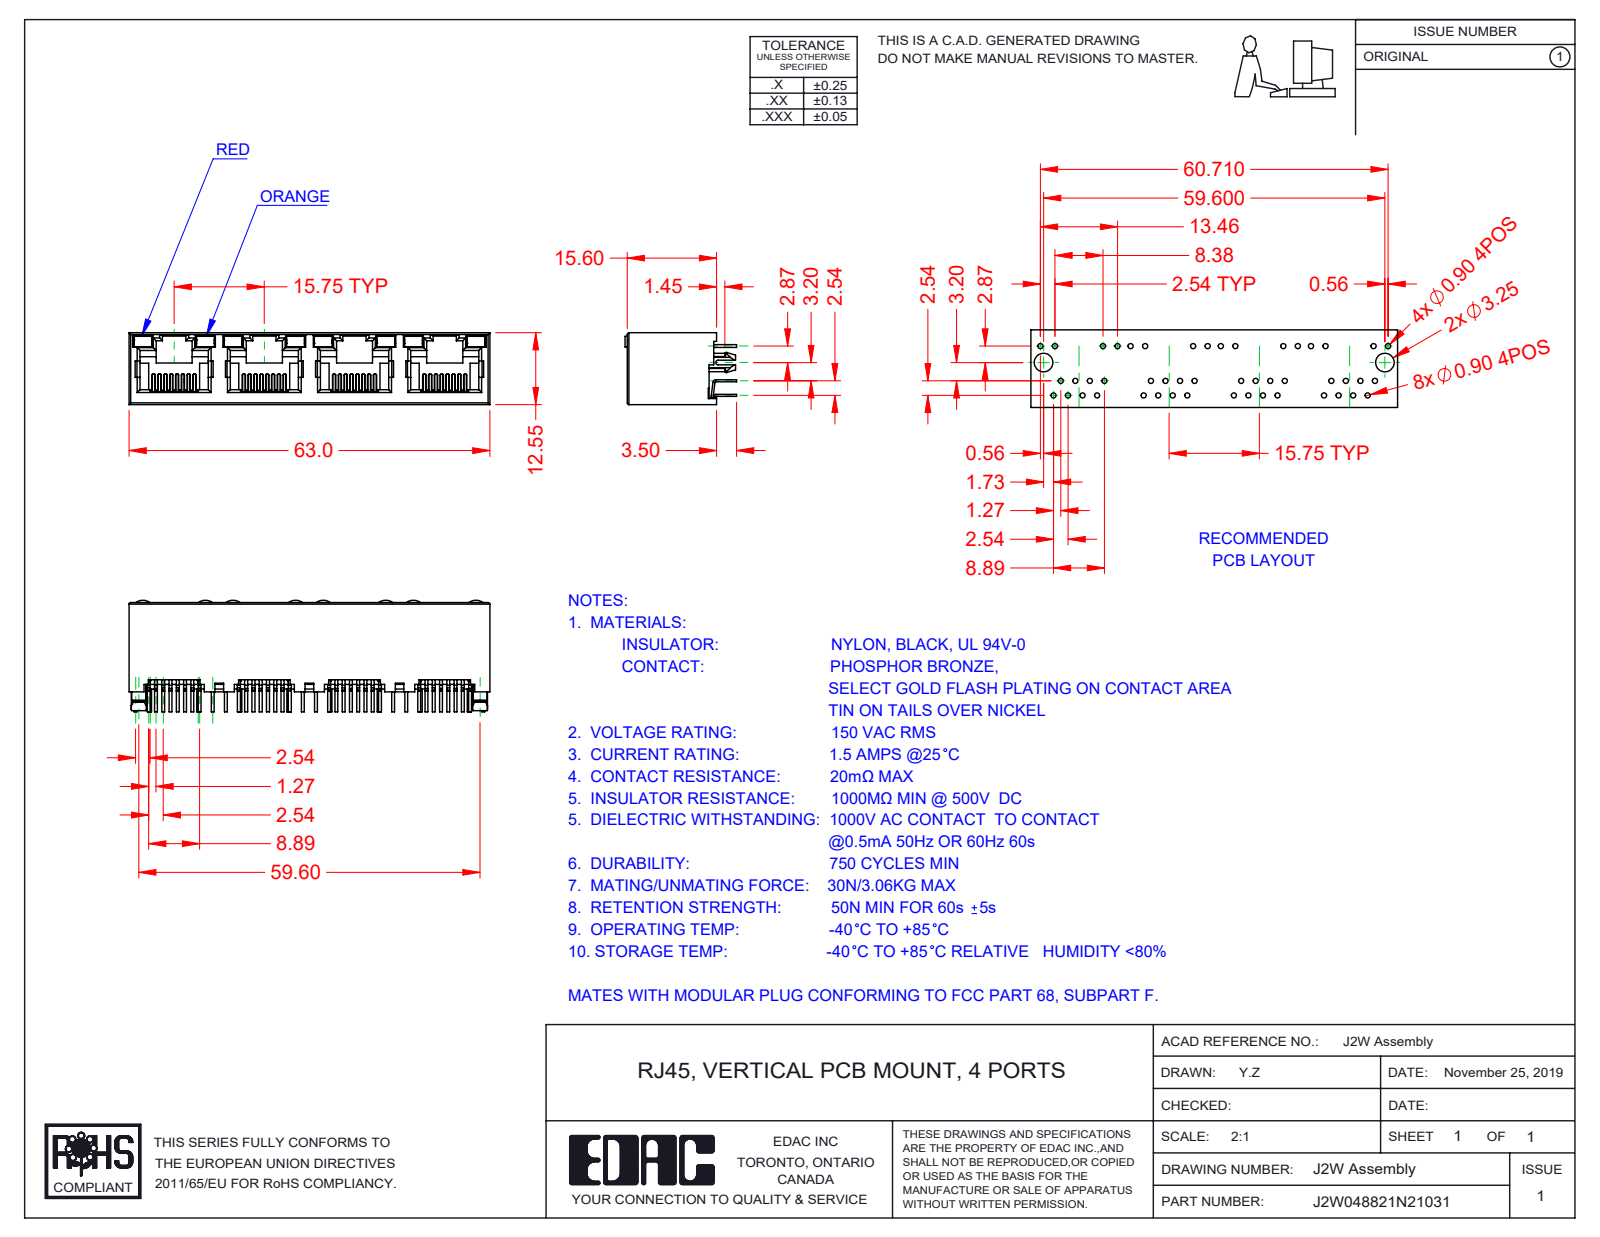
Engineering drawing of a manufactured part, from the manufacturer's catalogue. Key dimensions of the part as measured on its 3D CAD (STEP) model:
Part name (STEP PRODUCT): 2W LED RH_4-Orange; J2W048821N24131; 2W LED LH_2-Red; 2W Contacts (+2 more)
STEP written by: SolidWorks 2016 (CONFIG_CONTROL_DESIGN)
Units: millimetres
Bodies: 45 solids, 3135 faces (2600 planar, 477 cylindrical, 58 other)
Overall size (bounding box): 63 × 19.5 × 12.55
Volume: 5 335 mm³ · Surface area: 13 144 mm²
Partial cylindrical surfaces — rounded edges, fillets, slot ends (radius × count): R0.15 ×64, R0.2 ×29, R0.5 ×28, R0.3 ×14, R0.45 ×8, R2 ×8, R0.25 ×2, R1.5 ×2
Main face-to-face distances: 12.55, 11.9, 0.65, 15.75, 0.36, 1.5, 0.78, 0.6, 11.3, 31.5
